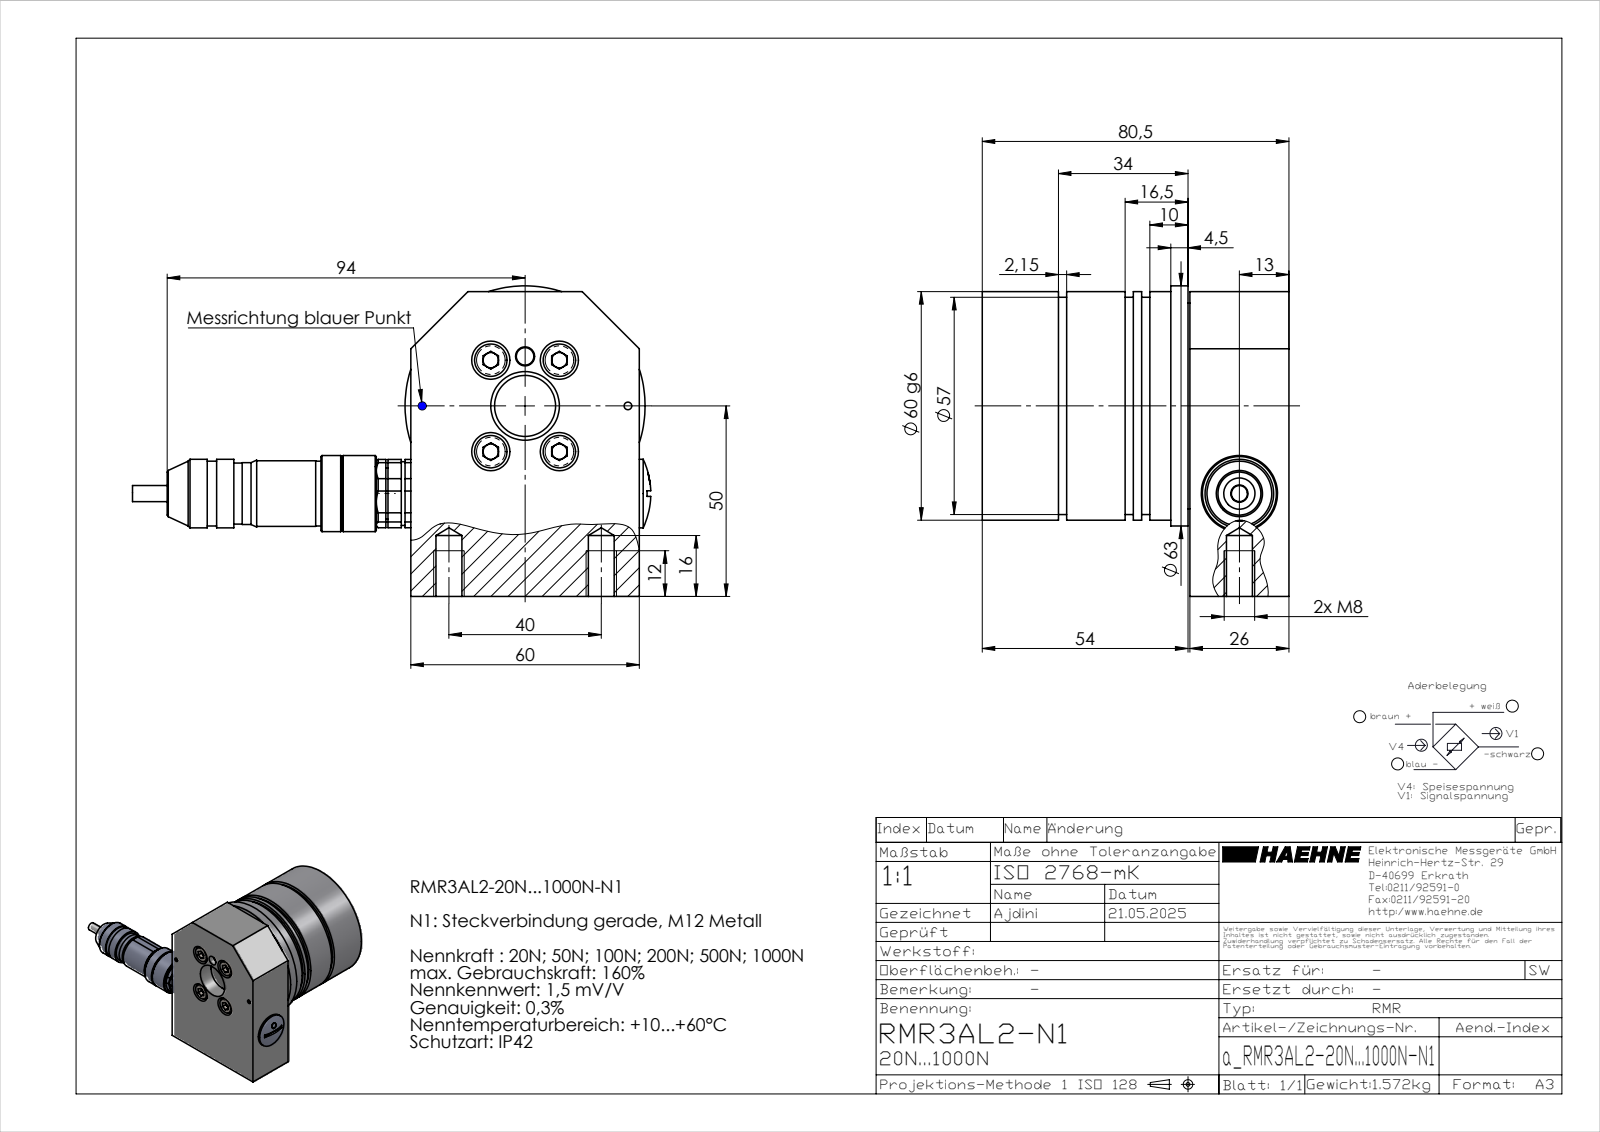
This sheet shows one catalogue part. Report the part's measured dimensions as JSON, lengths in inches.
{"part_name": "a_RMR3AL2-20N...1000N-N1", "step_written_by": "SolidWorks 2023 (AUTOMOTIVE_DESIGN)", "units": "inches", "bodies": {"solids": 16, "faces": 491, "planar": 248, "cylindrical": 156, "other": 87}, "overall_size": [5.356, 3.209, 3.169], "volume_in3": 14.85, "surface_area_in2": 116, "round_holes": [[0.039, 5], [0.165, 4], [0.209, 4], [0.394, 4], [0.079, 2], [0.268, 2], [0.025, 1], [0.118, 1], [0.177, 1], [0.197, 1], [0.323, 1], [0.33, 1]], "round_bosses_or_shafts": [[0.034, 5], [0.335, 4], [0.197, 4], [0.059, 4], [0.039, 4], [2.48, 1], [2.362, 1], [2.244, 1]], "partial_cylinders_radius": [[0.012, 6], [0.039, 4], [0.022, 1], [0.024, 1], [0.03, 1], [0.138, 1], [0.945, 1], [1.575, 1]], "face_to_face_distances": [0.453, 1.909, 1.457, 2.874, 2.146, 2.441, 0.433, 1.85, 0.591, 1.024], "hole_center_spacings": [0.098, 0.139, 0.591, 0.852, 1.494, 0.197, 0.357, 0.709]}
